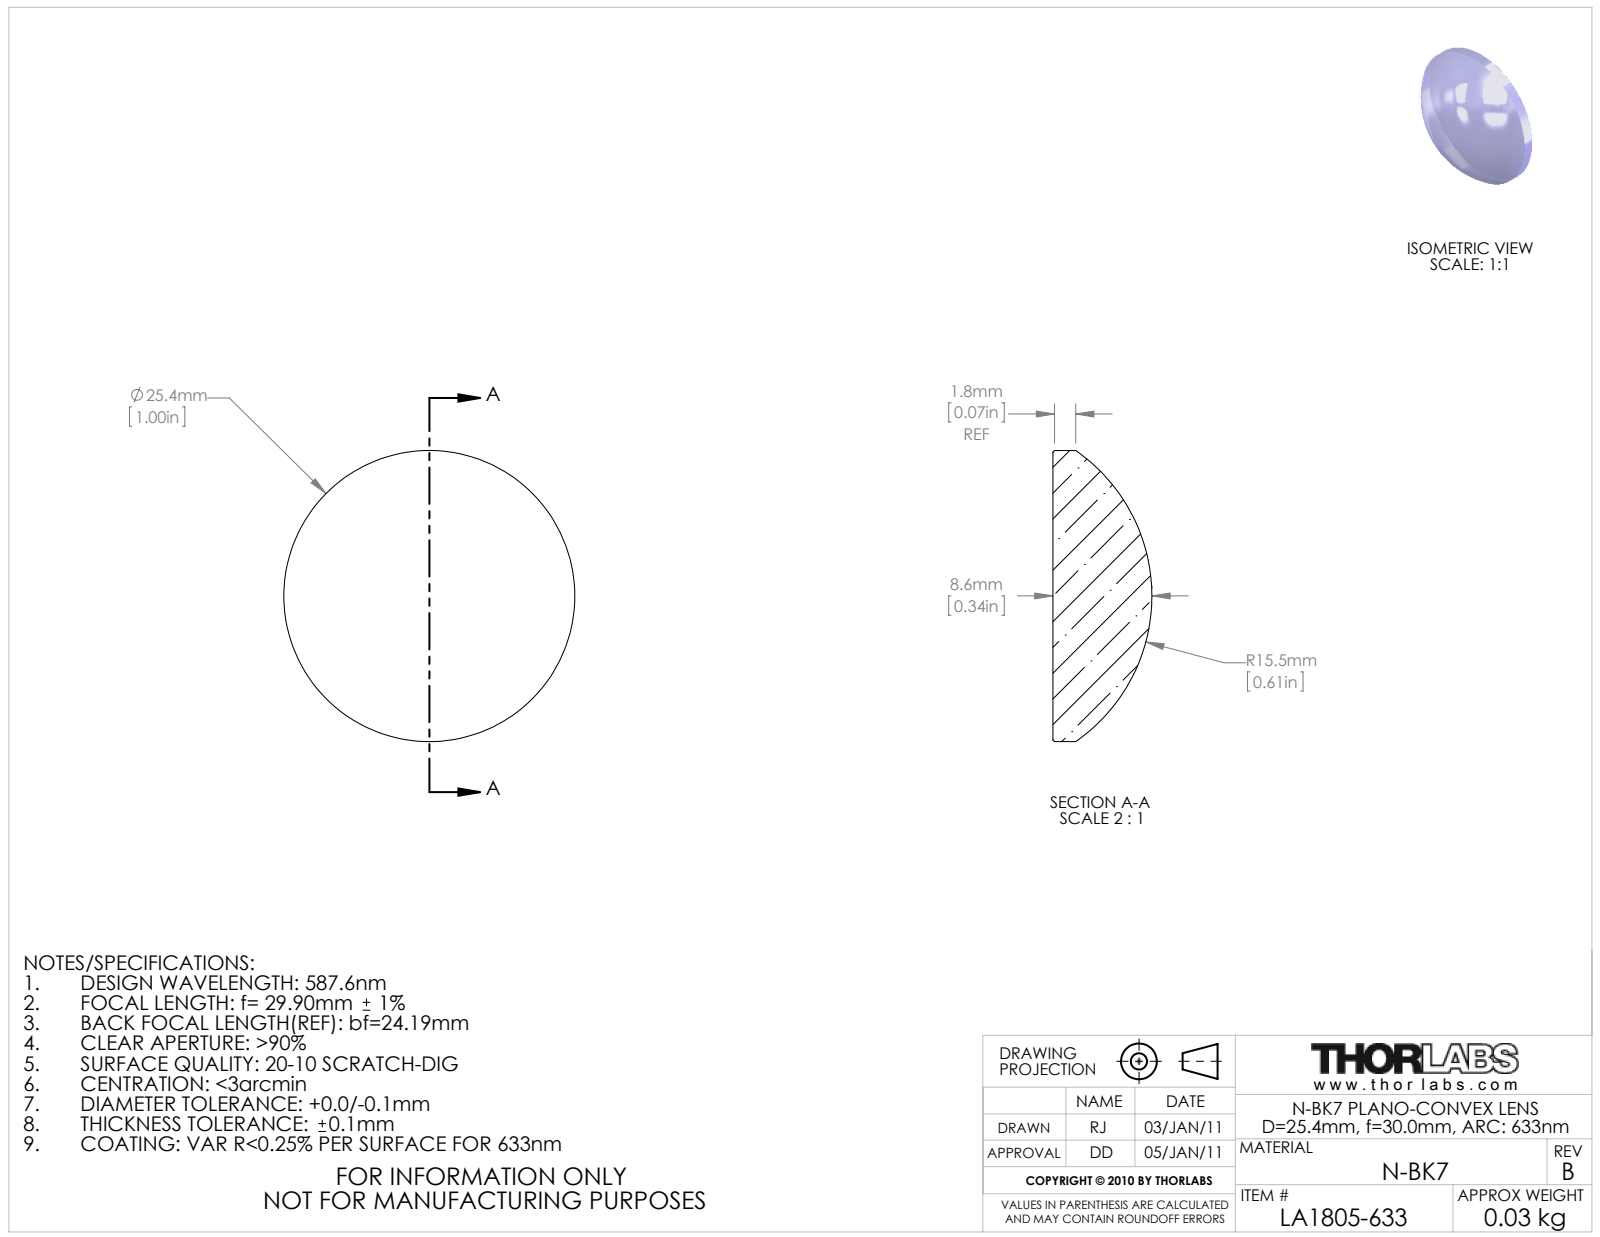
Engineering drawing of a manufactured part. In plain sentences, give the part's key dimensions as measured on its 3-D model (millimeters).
The part is named "21783-E0W". Its 3-D file was written by "SolidWorks 2011 (AUTOMOTIVE_DESIGN)". It is 0 solids with 7 faces: 1 planar, 2 cylindrical and 4 other. Overall it measures 25.4 by 25.4 by 8.64 millimeters. Round bosses or shafts: 1 of diameter 25.4.
